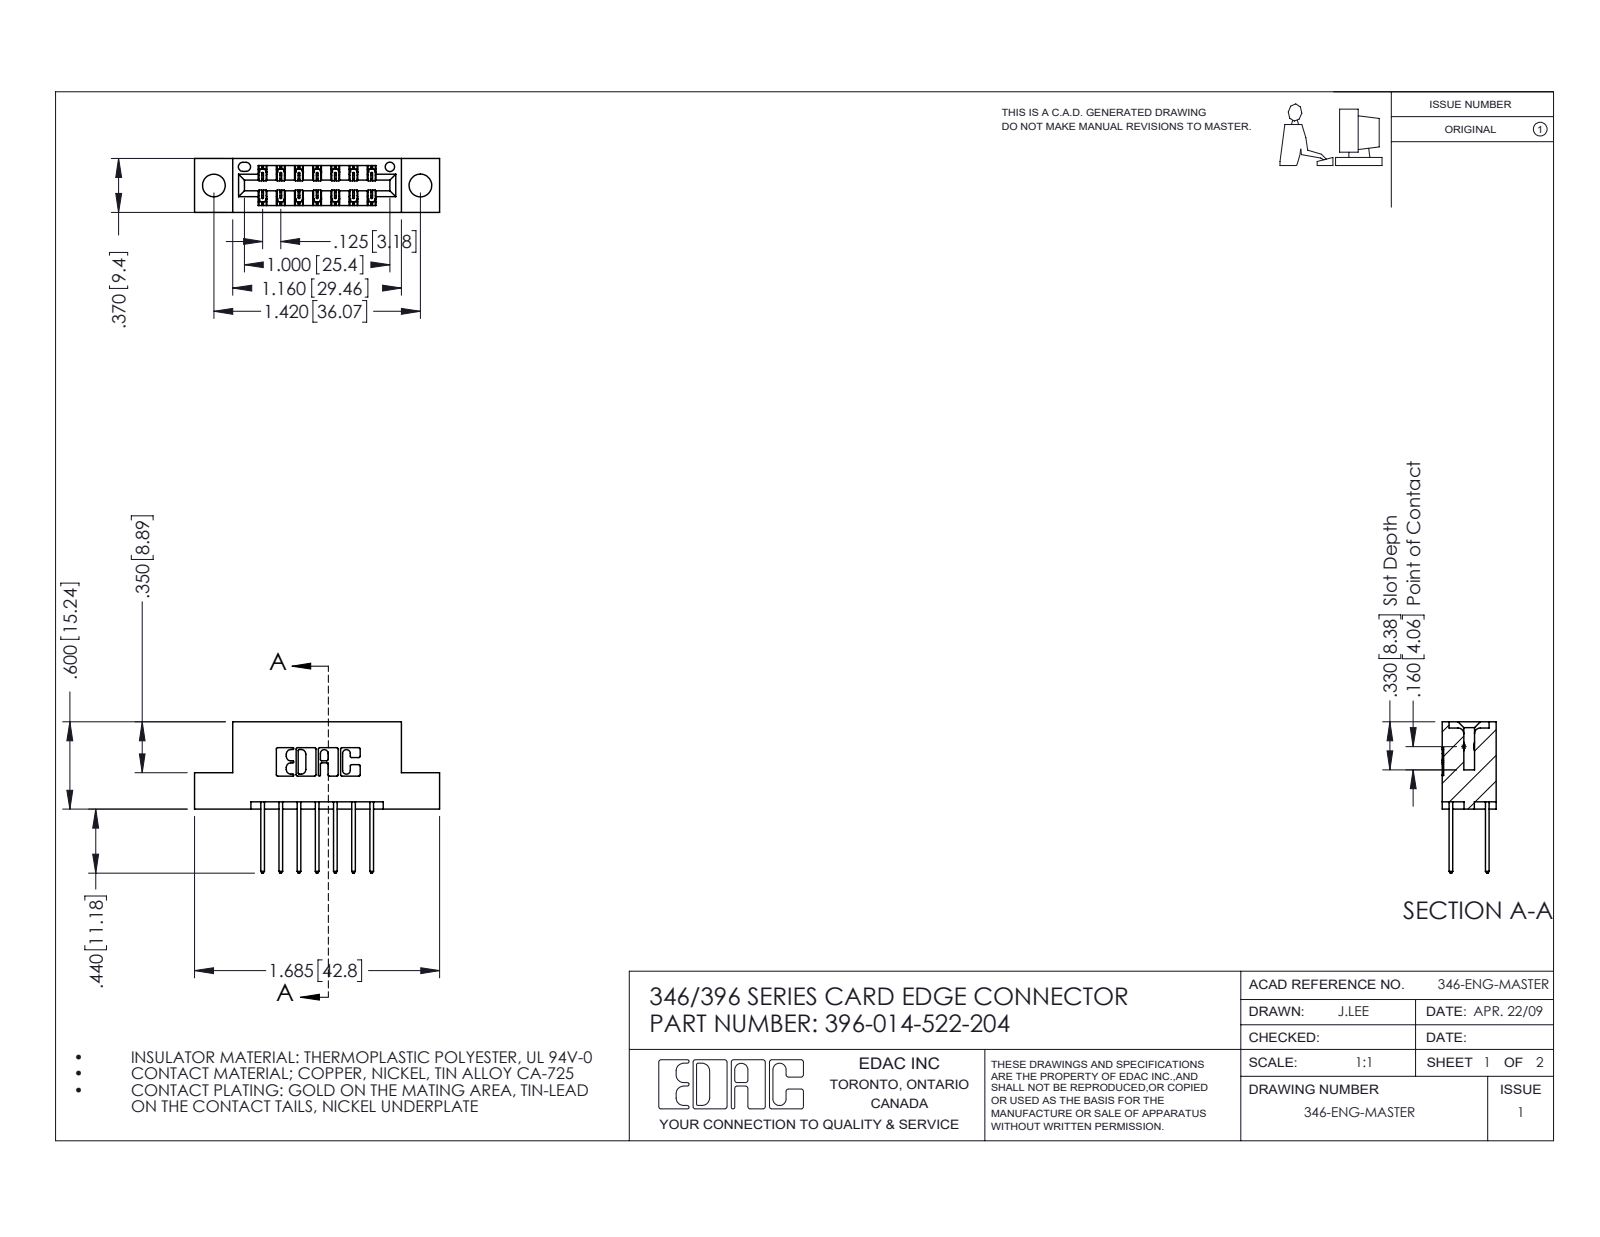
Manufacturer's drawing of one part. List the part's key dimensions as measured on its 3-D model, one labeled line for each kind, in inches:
Part name (STEP PRODUCT): 345-292-001_345-293-122; 396-014-522-204; 346 Part_Flush Mounting Lugs - 0.156 Dia-TH
STEP written by: SolidWorks 2016 (CONFIG_CONTROL_DESIGN)
Units: inches
Bodies: 15 solids, 850 faces (566 planar, 284 cylindrical, 0 other)
Overall size (bounding box): 1.685 × 1.04 × 0.37
Volume: 0.235 in³ · Surface area: 7.318 in²
Round holes (diameter × count): ⌀0.156 ×2, ⌀0.064 ×1
Partial cylindrical surfaces — rounded edges, fillets, slot ends (radius × count): R0.01 ×22, R0.006 ×21, R0.01 ×14, R0.007 ×6, R0.031 ×6, R0.026 ×3, R0.014 ×2, R0.022 ×2
Main face-to-face distances: 0.25, 0.048, 0.322, 0.37, 0.025, 0.072, 0.298, 0.275, 0.148, 0.222
Hole centre spacings: 0.246, 1.217, 1.42
